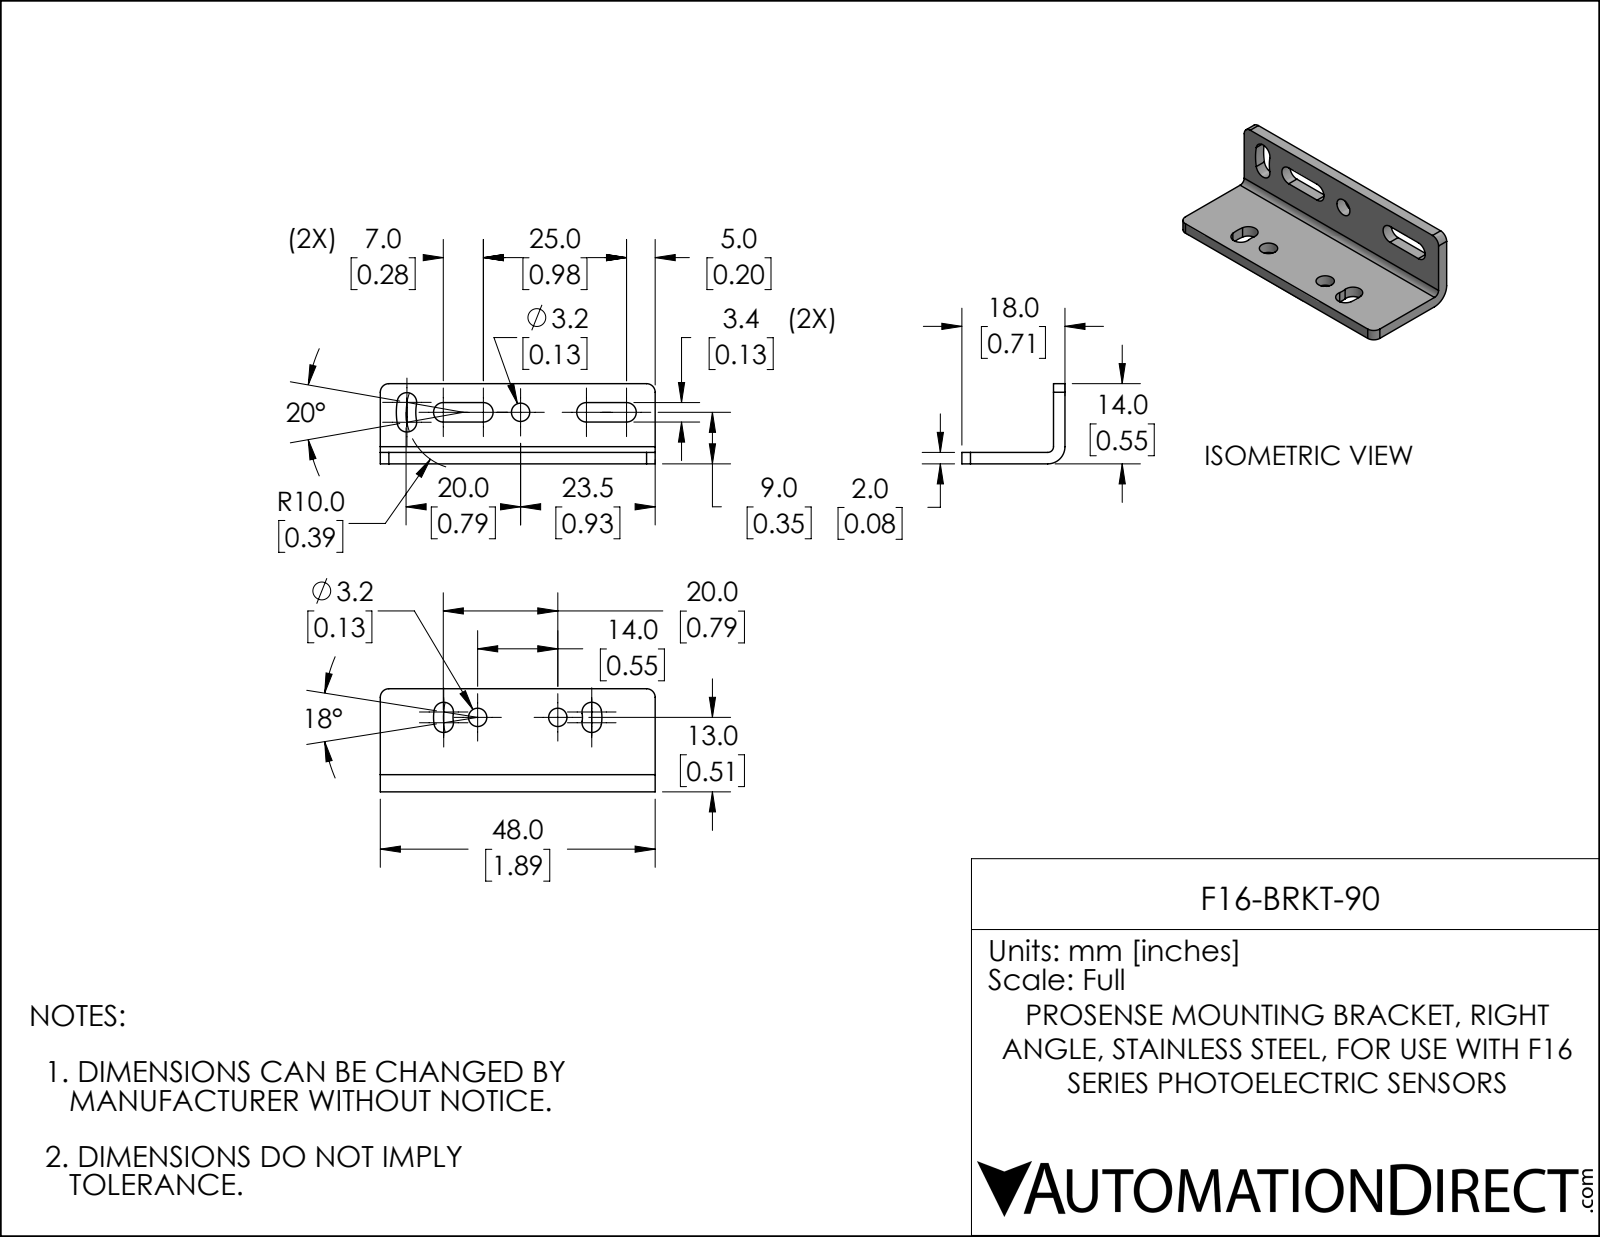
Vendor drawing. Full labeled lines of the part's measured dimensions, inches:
Part name (STEP PRODUCT): F16-BRKT-90
STEP written by: SolidWorks 2019 (CONFIG_CONTROL_DESIGN)
Units: inches
Bodies: 1 solid, 37 faces (12 planar, 25 cylindrical, 0 other)
Overall size (bounding box): 1.89 × 0.709 × 0.551
Volume: 0.153 in³ · Surface area: 4.752 in²
Round holes (diameter × count): ⌀0.126 ×3
Partial cylindrical surfaces — rounded edges, fillets, slot ends (radius × count): R0.067 ×10, R0.059 ×4, R0.169 ×2, R0.303 ×2, R0.039 ×1, R0.118 ×1, R0.327 ×1, R0.461 ×1
Main face-to-face distances: 0.079, 0.551, 0.472, 0.709, 0.63, 1.89, 0.287, 0.421, 0.209, 0.343
Hole centre spacings: 0.551
